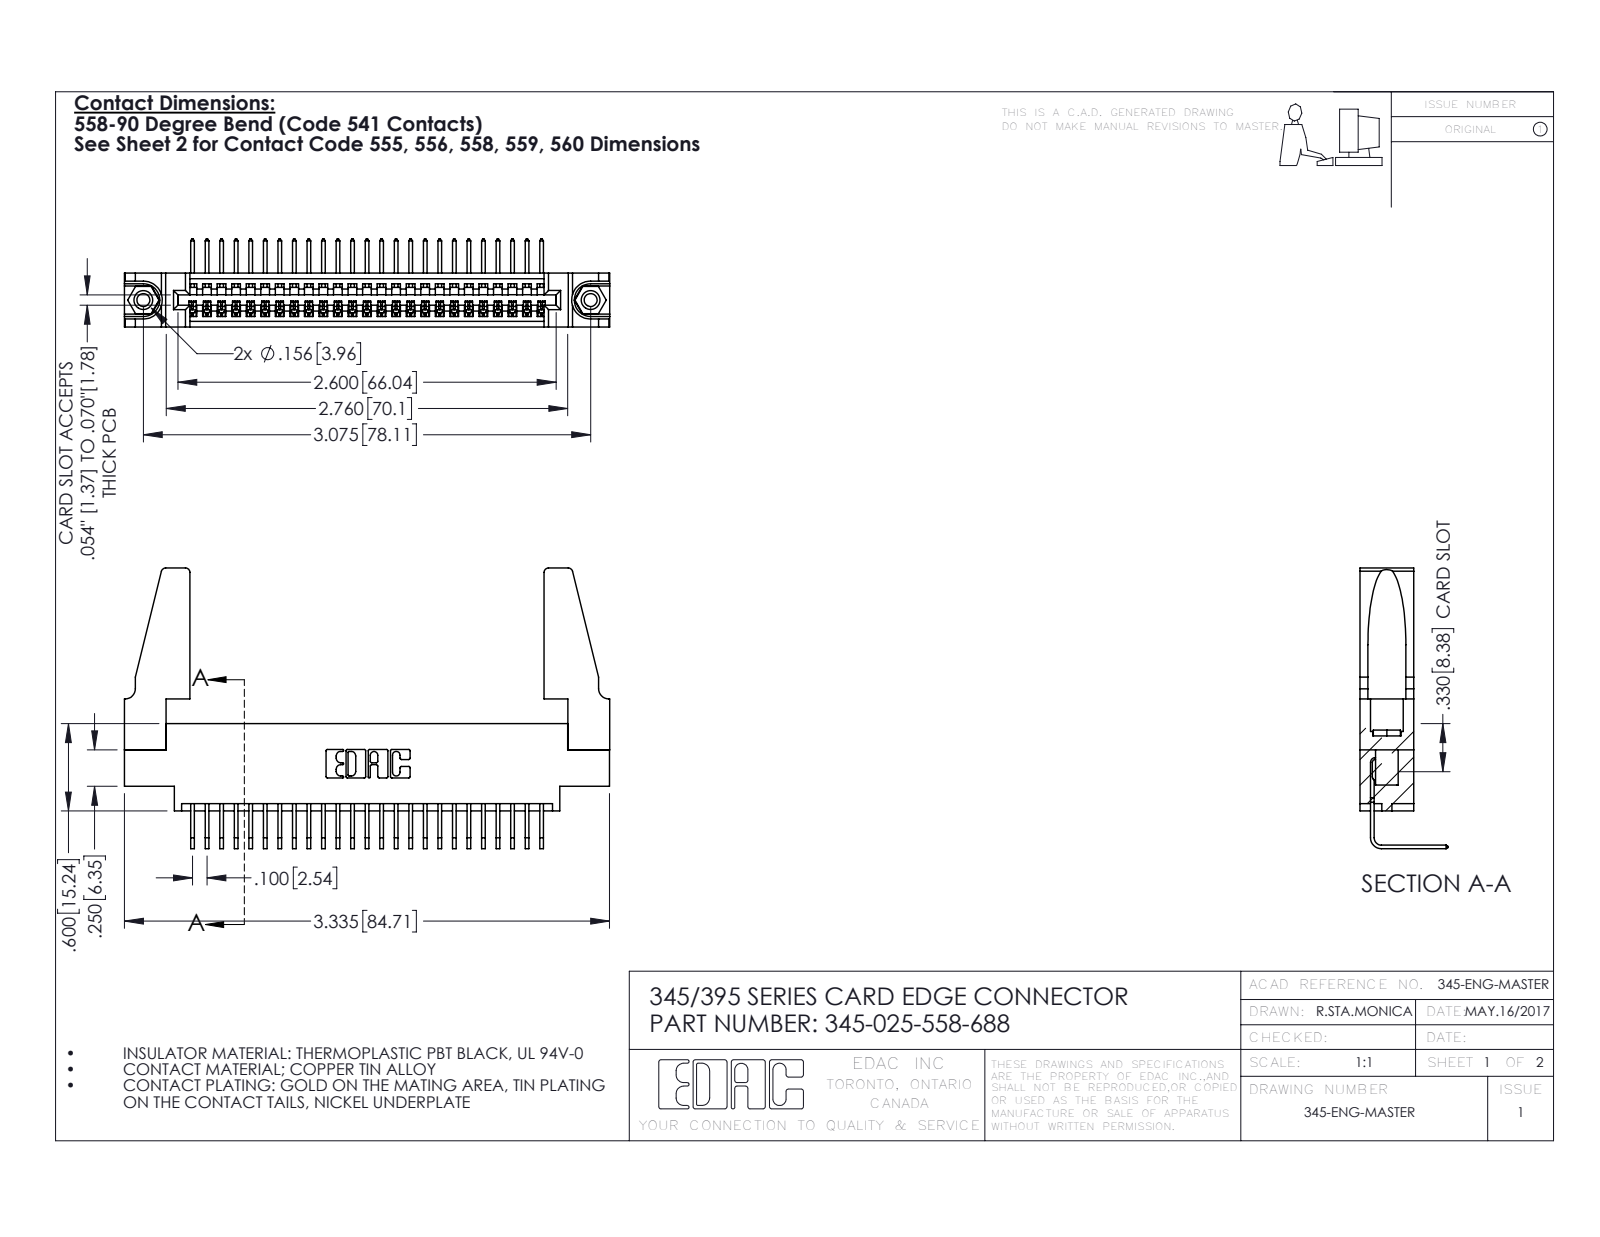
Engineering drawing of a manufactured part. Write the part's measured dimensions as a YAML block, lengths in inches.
part_name: "345-250-001_345-250-001-102; 345-025-558-688; 345-220-078_345-220-088; 345 Part_0.170 Offset - 0.156 Dia-TH (+1 more)"
step_written_by: "SolidWorks 2016 (CONFIG_CONTROL_DESIGN)"
units: inches
bodies: {solids: 30, faces: 1754, planar: 1206, cylindrical: 532, other: 16}
overall_size: [3.336, 1.929, 0.605]
volume: 0.679
surface_area: 21.68
round_holes:
  - {diameter: 0.089, count: 2}
  - {diameter: 0.125, count: 2}
  - {diameter: 0.156, count: 2}
  - {diameter: 0.064, count: 1}
round_bosses_or_shafts:
  - {diameter: 0.155, count: 2}
partial_cylinders:
  - {radius: 0.006, count: 50}
  - {radius: 0.01, count: 22}
  - {radius: 0.03, count: 8}
  - {radius: 0.007, count: 6}
  - {radius: 0.031, count: 6}
  - {radius: 0.026, count: 3}
  - {radius: 0.031, count: 2}
  - {radius: 0.04, count: 2}
face_to_face_distances: [0.37, 0.072, 0.298, 0.2, 0.098, 0.272, 0.025, 0.225, 0.175, 0.149]
hole_center_spacings: [0.27, 2.84, 3.075]
